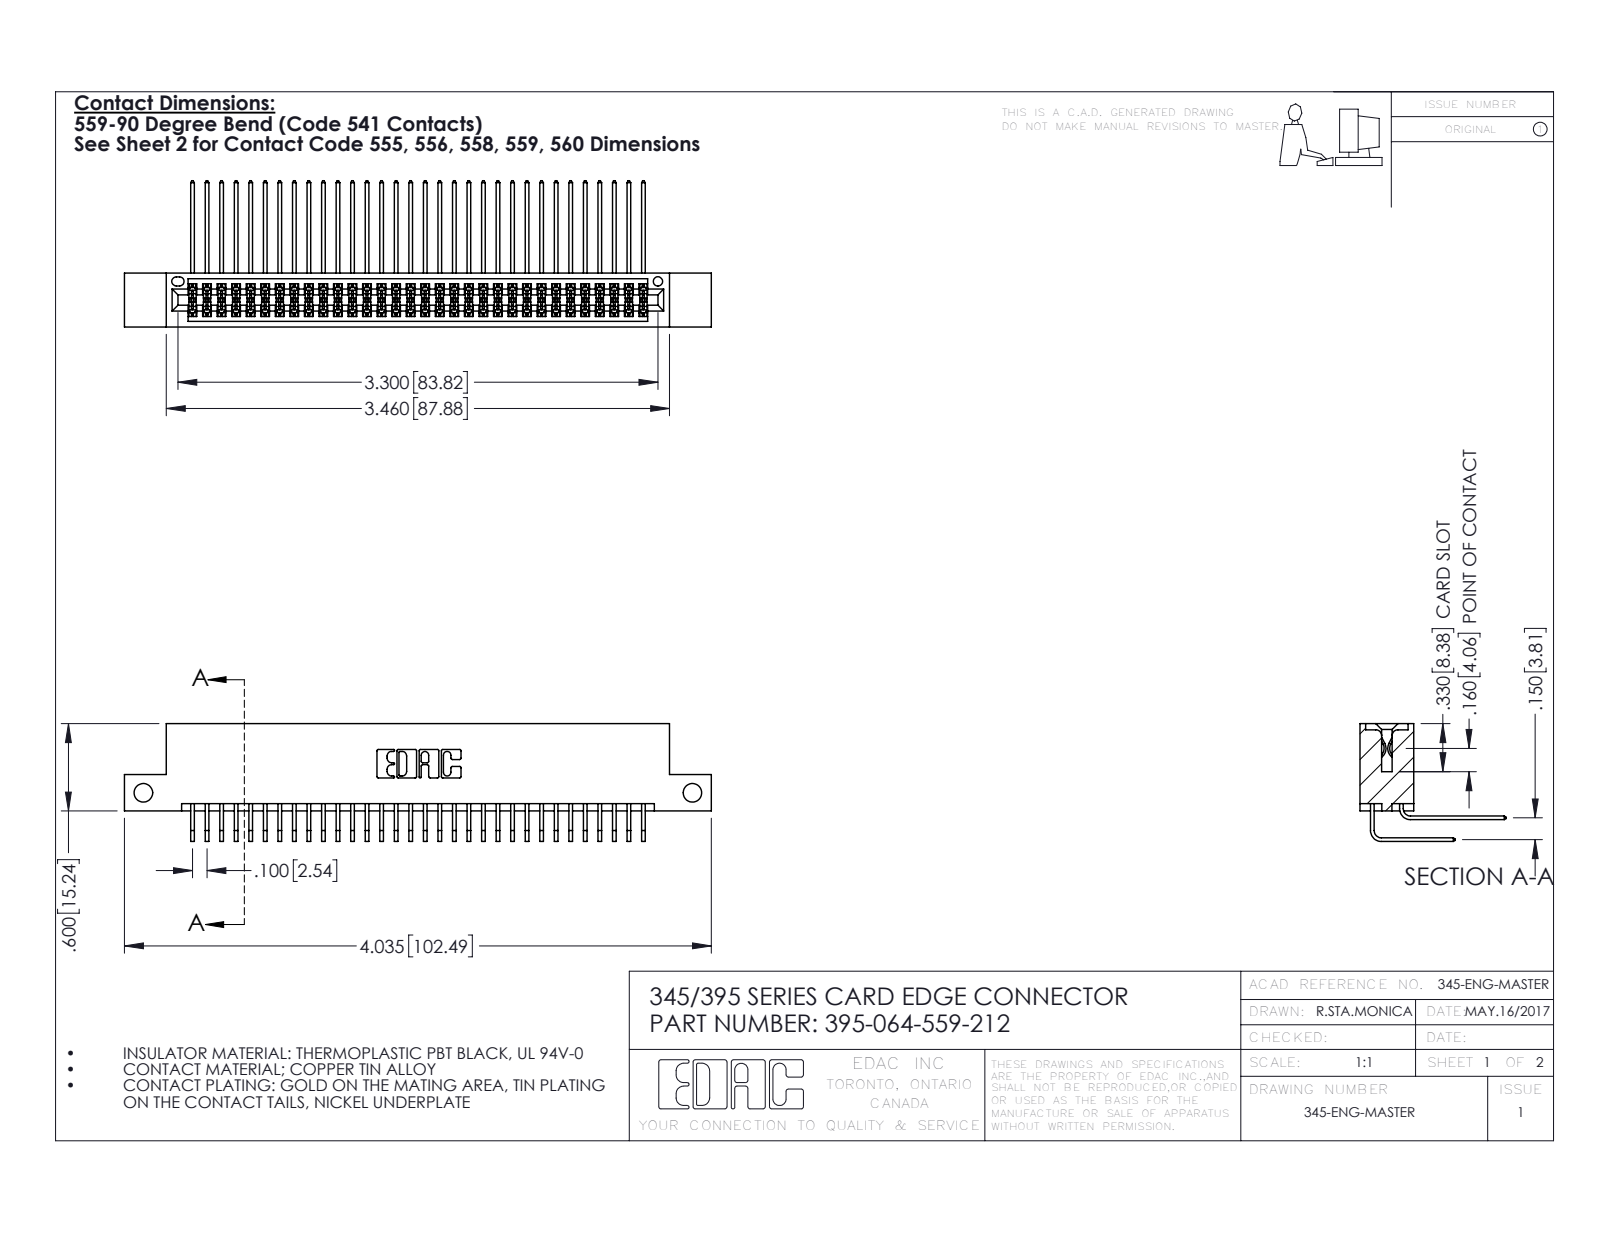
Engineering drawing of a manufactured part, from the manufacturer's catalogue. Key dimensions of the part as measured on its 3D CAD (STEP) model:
Part name (STEP PRODUCT): 345 Part_Flush Mounting Lugs - Side Mount; 345-292-001_558 559 Tail - 1; 395-064-559-212; 345-292-001_559 Tail - 2
STEP written by: SolidWorks 2016 (CONFIG_CONTROL_DESIGN)
Units: inches
Bodies: 65 solids, 3454 faces (2320 planar, 1134 cylindrical, 0 other)
Overall size (bounding box): 4.035 × 1.005 × 0.809
Volume: 0.619 in³ · Surface area: 25.42 in²
Round holes (diameter × count): ⌀0.128 ×2, ⌀0.064 ×1
Partial cylindrical surfaces — rounded edges, fillets, slot ends (radius × count): R0.006 ×97, R0.01 ×22, R0.007 ×6, R0.031 ×6, R0.026 ×3, R0.014 ×2, R0.019 ×2, R0.022 ×2
Main face-to-face distances: 0.072, 0.298, 0.2, 0.37, 0.098, 0.272, 0.025, 0.225, 0.175, 0.15
Hole centre spacings: 3.775
